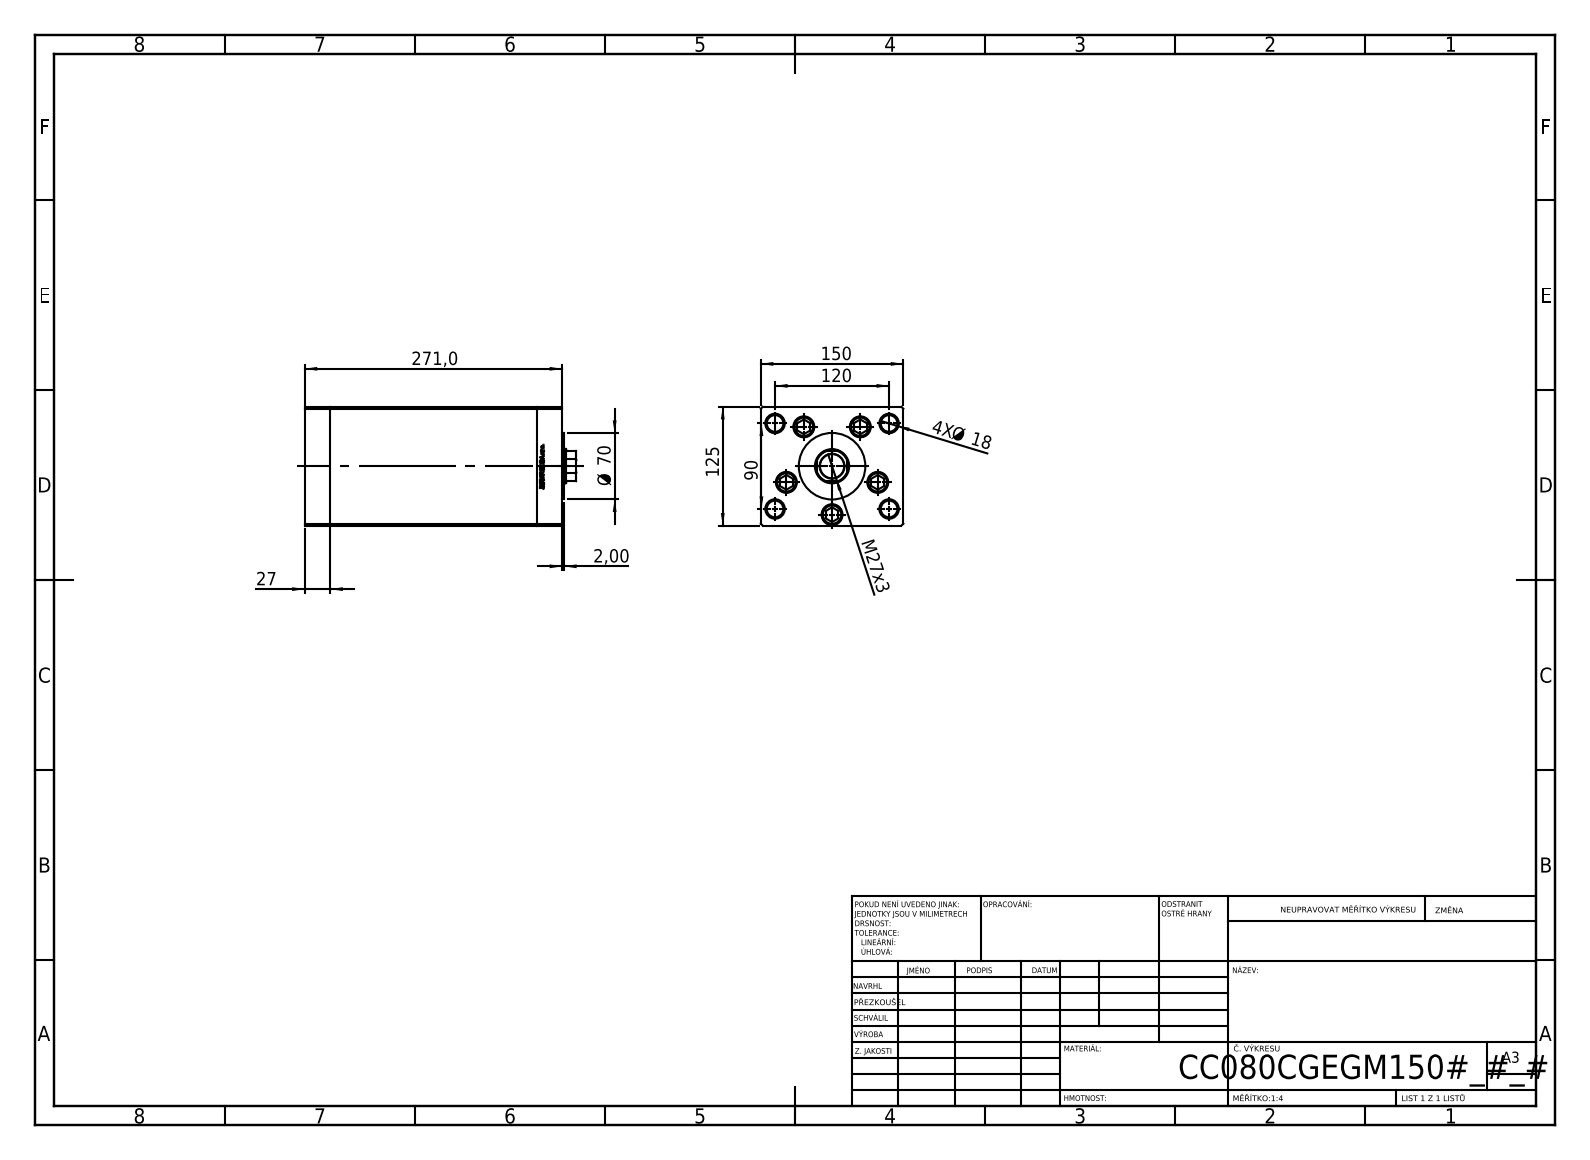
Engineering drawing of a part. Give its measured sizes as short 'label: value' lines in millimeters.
name: V220C FRONT; V220C_C MIDDLE; V220C_VC_C; ALLEN BOLT (+1 more)
written by: SolidWorks 2019 (CONFIG_CONTROL_DESIGN)
unit: mm
bodies: 13 solids, 1163 faces (542 planar, 159 cylindrical, 462 other)
size: 286 × 150 × 125
volume: 4 127 000 mm³; area: 449 865 mm²
holes: 9× ⌀17.5, 5× ⌀22, 4× ⌀16, 4× ⌀20.5, 1× ⌀21, 1× ⌀25.5, 1× ⌀36
bosses: 5× ⌀8, 4× ⌀21, 1× ⌀80, 1× ⌀70
rounds: 2× R0.93, 1× R17.5
face distances: 150, 125, 27, 244, 217, 33.5, 6.5, 271, 237.5, 210.5
hole spacings: 51, 75, 30.43, 30.48, 58.89, 60.3, 61.25, 63.14
